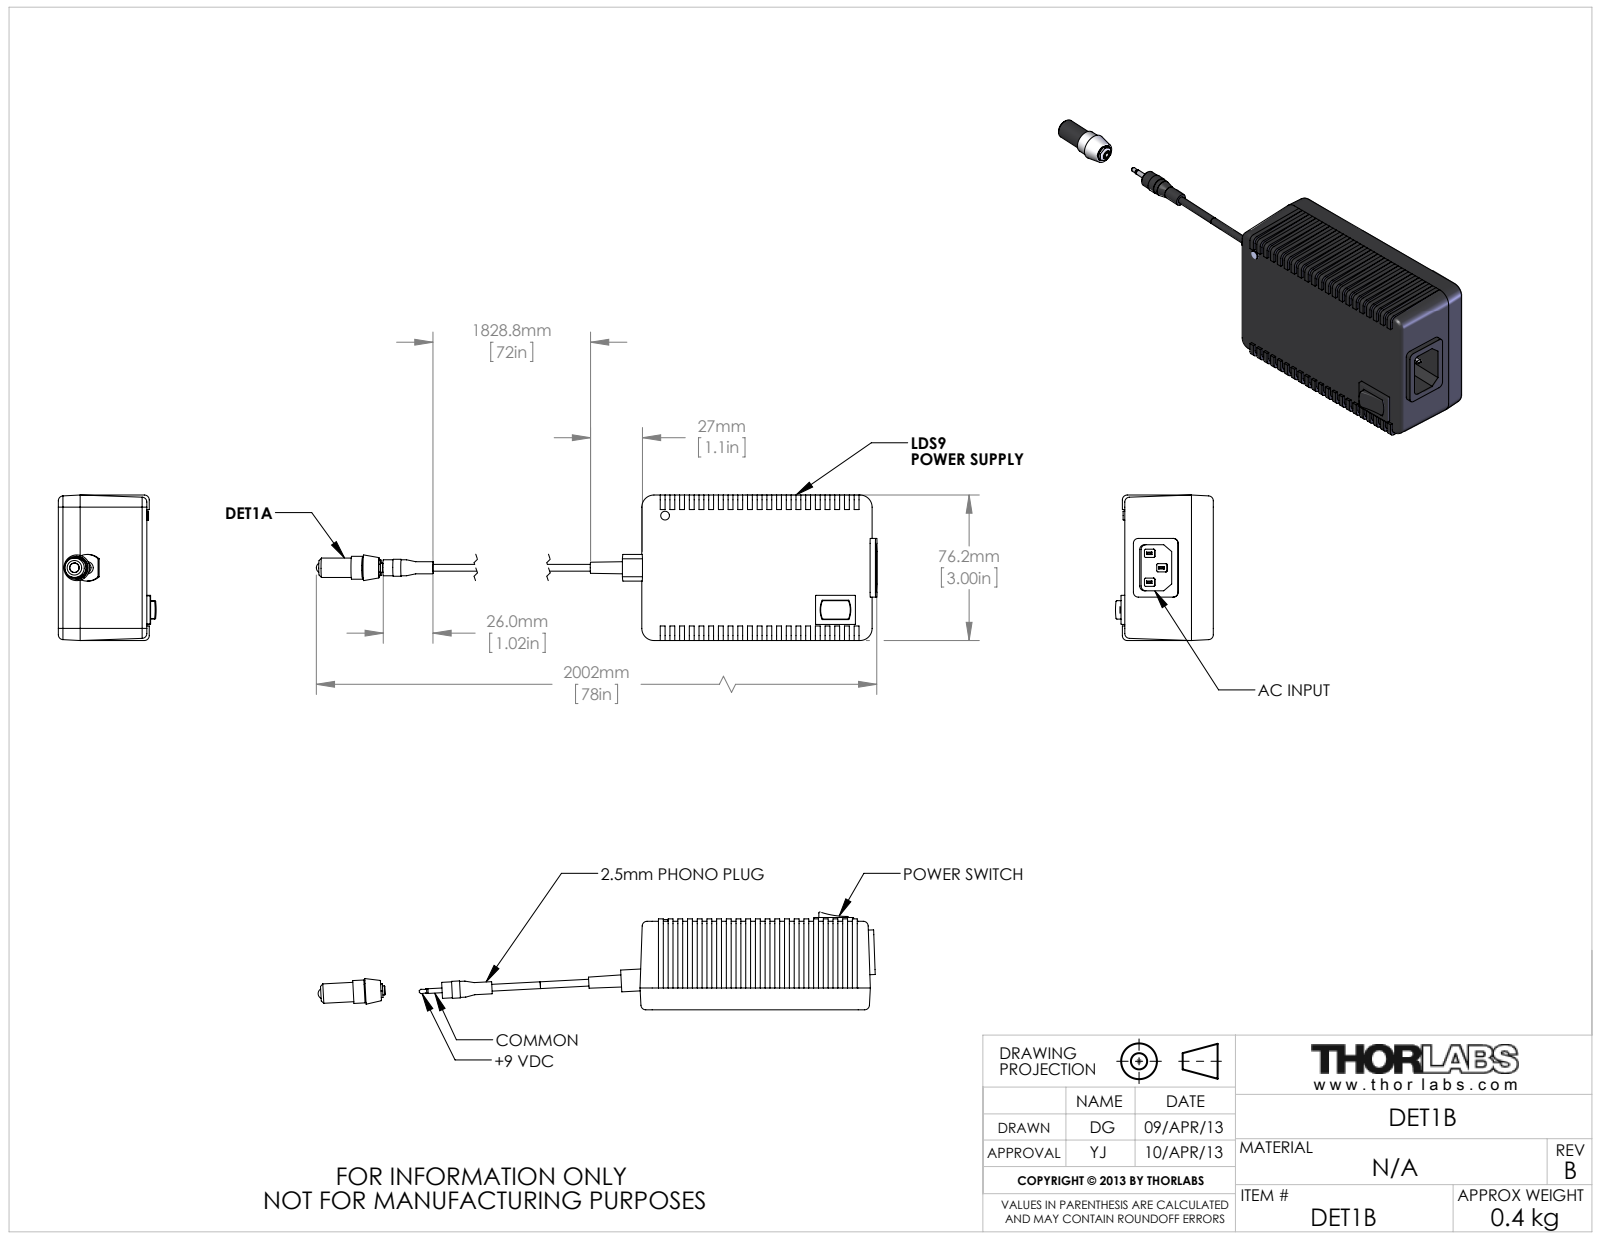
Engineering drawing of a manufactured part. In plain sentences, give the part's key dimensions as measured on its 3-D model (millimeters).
The part is named "18911-E0W". Its 3-D file was written by "SolidWorks 2012 (AUTOMOTIVE_DESIGN)". It is 0 solids with 609 faces: 352 planar, 167 cylindrical and 90 other. Overall it measures 261.96 by 76.2 by 51.23 millimeters. Round holes: 1 of diameter 2.5, 1 of diameter 4.95, 1 of diameter 8.89, 1 of diameter 10.29. Round bosses or shafts: 2 of diameter 3.56, 1 of diameter 11.99, 1 of diameter 10.16, 1 of diameter 8.89, 1 of diameter 8.38, 1 of diameter 7.94, 1 of diameter 6.35, 1 of diameter 4.72. Partial cylindrical surfaces (rounded edges, fillets, slot ends): 16 of radius 2.54, 12 of radius 0.64, 8 of radius 0.25, 4 of radius 0.51, 2 of radius 8.29, 2 of radius 12.56, 2 of radius 12.81, 1 of radius 44.87. The main face-to-face distances are 46.35, 76.2, 5.08, 10.16, 15.24, 20.32, 25.4, 30.48, 35.56, 40.64.
